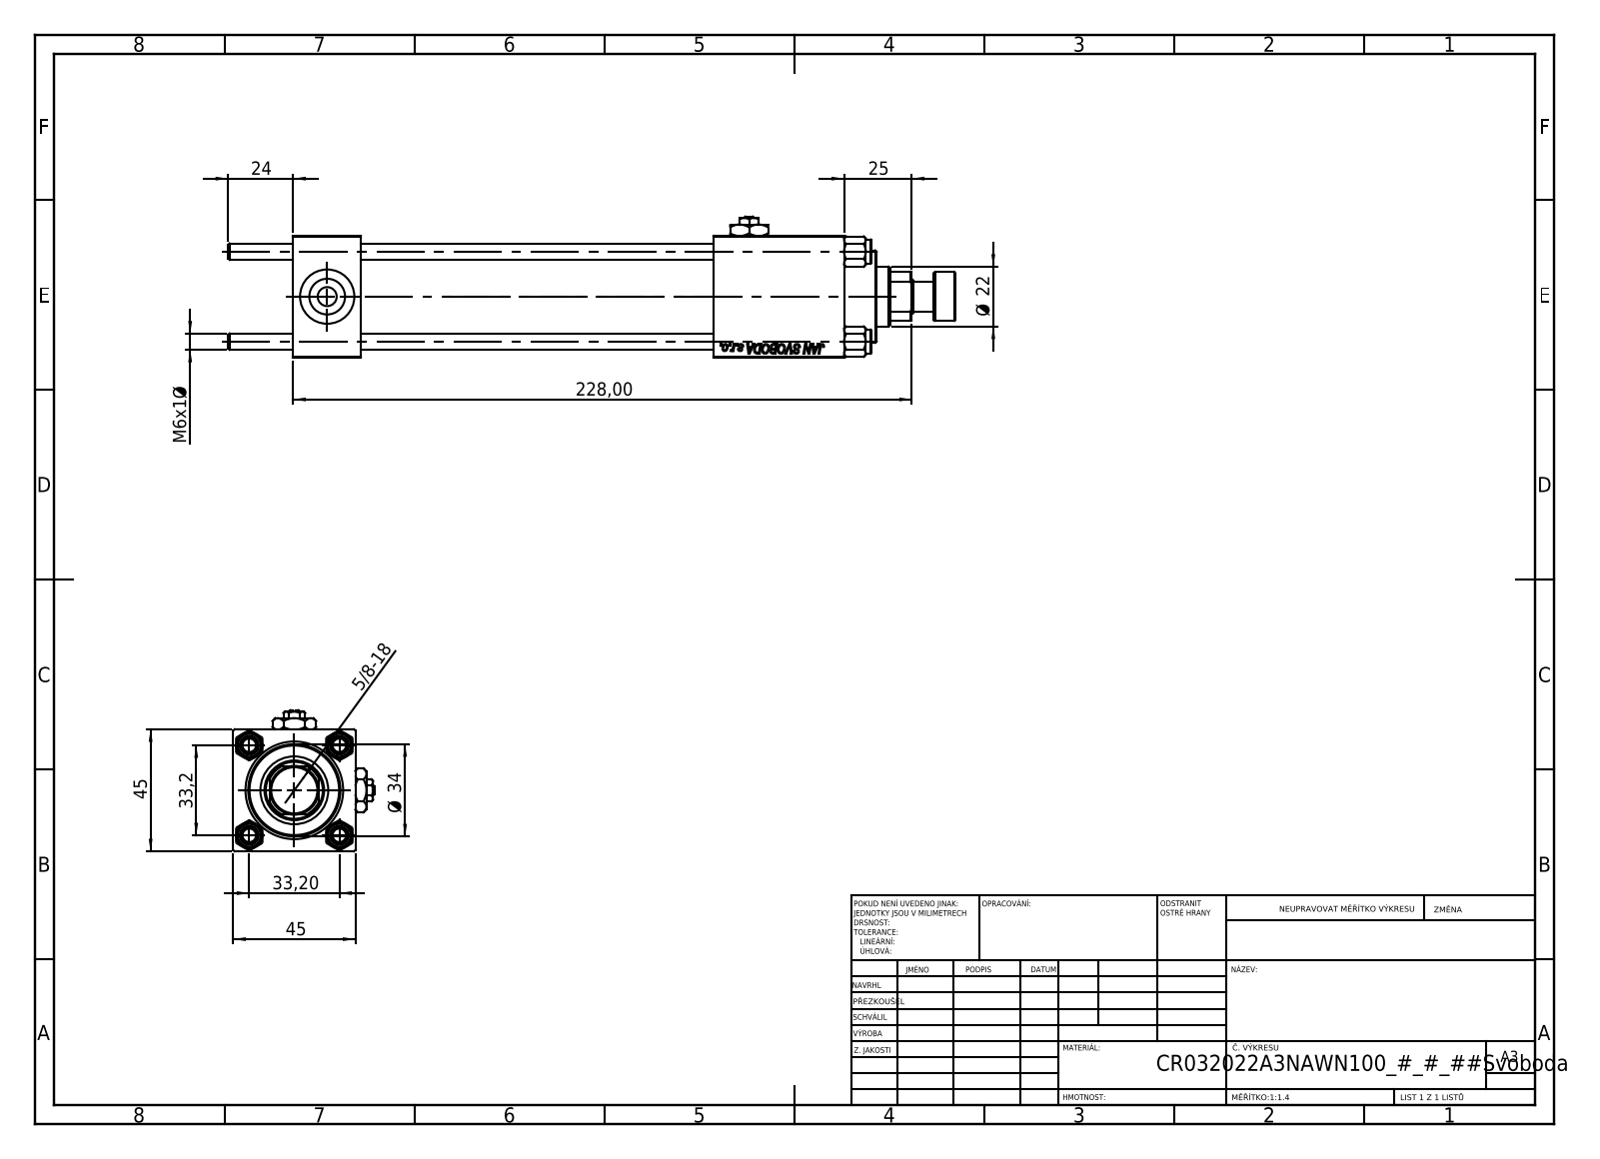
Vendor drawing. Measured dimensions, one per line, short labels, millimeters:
name: Zatka_pro_OIL_PORT; NUT_M5; V215CR_ROD_END_W; V215_VC_A (+3 more)
written by: SolidWorks 2019 (CONFIG_CONTROL_DESIGN)
unit: mm
bodies: 14 solids, 1246 faces (568 planar, 94 cylindrical, 584 other)
size: 268 × 52 × 52
volume: 281 001 mm³; area: 109 368 mm²
holes: 4× ⌀6, 2× ⌀7, 2× ⌀13.16, 2× ⌀20, 1× ⌀10.5, 1× ⌀13, 1× ⌀22, 1× ⌀24, 1× ⌀25, 1× ⌀32, 1× ⌀33
bosses: 4× ⌀9, 1× ⌀38, 1× ⌀34, 1× ⌀18, 1× ⌀11
rounds: 1× R10.5
face distances: 45, 25, 203, 155, 130, 178, 48, 44.8, 174.3, 149.3
hole spacings: 23.48, 33.2, 46.95
